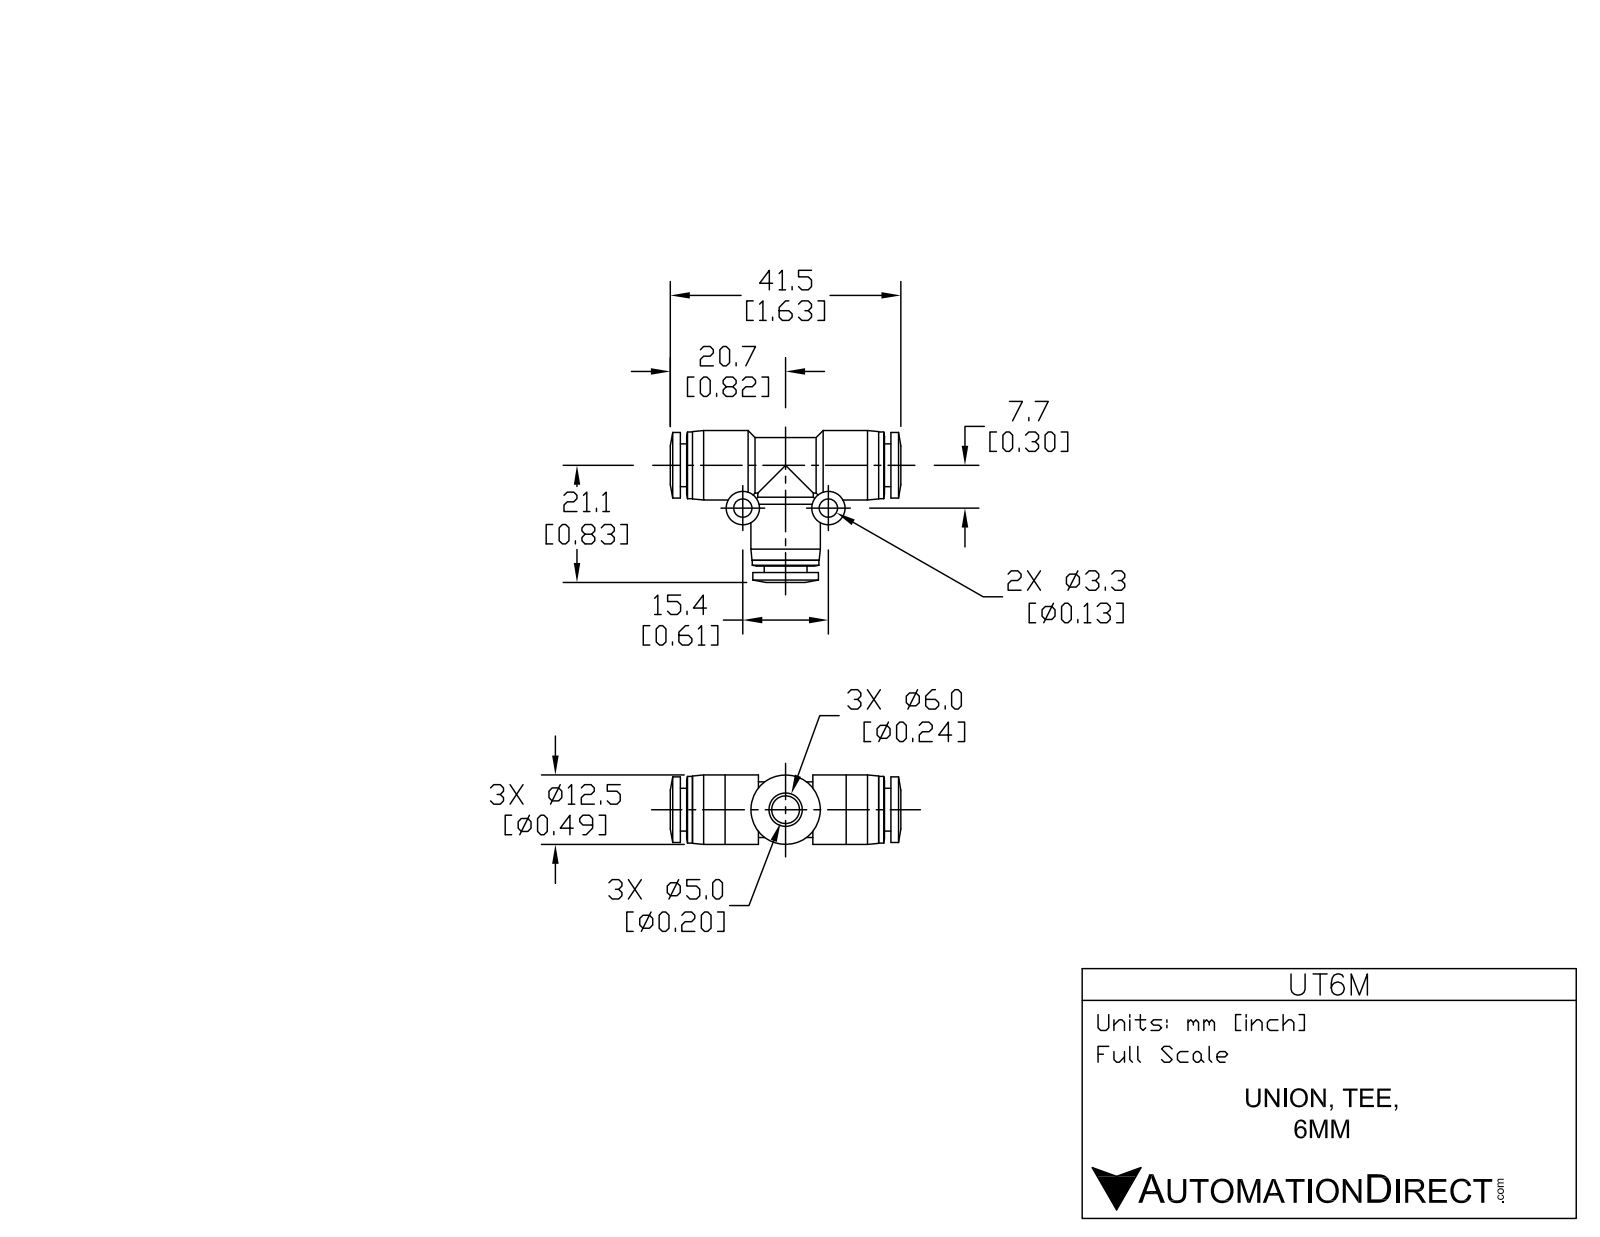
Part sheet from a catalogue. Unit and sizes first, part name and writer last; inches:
Units: inches
Overall size (bounding box): 1.634 × 1.073 × 0.492
Round holes (diameter × count): ⌀0.13 ×2, ⌀0.197 ×2, ⌀0.246 ×2
Round bosses / shafts (diameter × count): ⌀0.492 ×2, ⌀0.472 ×2, ⌀0.465 ×2, ⌀0.394 ×2, ⌀0.303 ×2, ⌀0.236 ×2
Main face-to-face distances: 0.045, 1.447, 1.492, 0.492, 1.402, 0.575, 0.53, 0.917, 0.872, 0.071
Hole centre spacings: 0.622
Volume: 0.29 in³ · Surface area: 6.789 in²
Bodies: 1 solid, 95 faces (19 planar, 46 cylindrical, 30 other)
Part name (STEP PRODUCT): UT6M
STEP written by: SolidWorks 2015 (AUTOMOTIVE_DESIGN)
